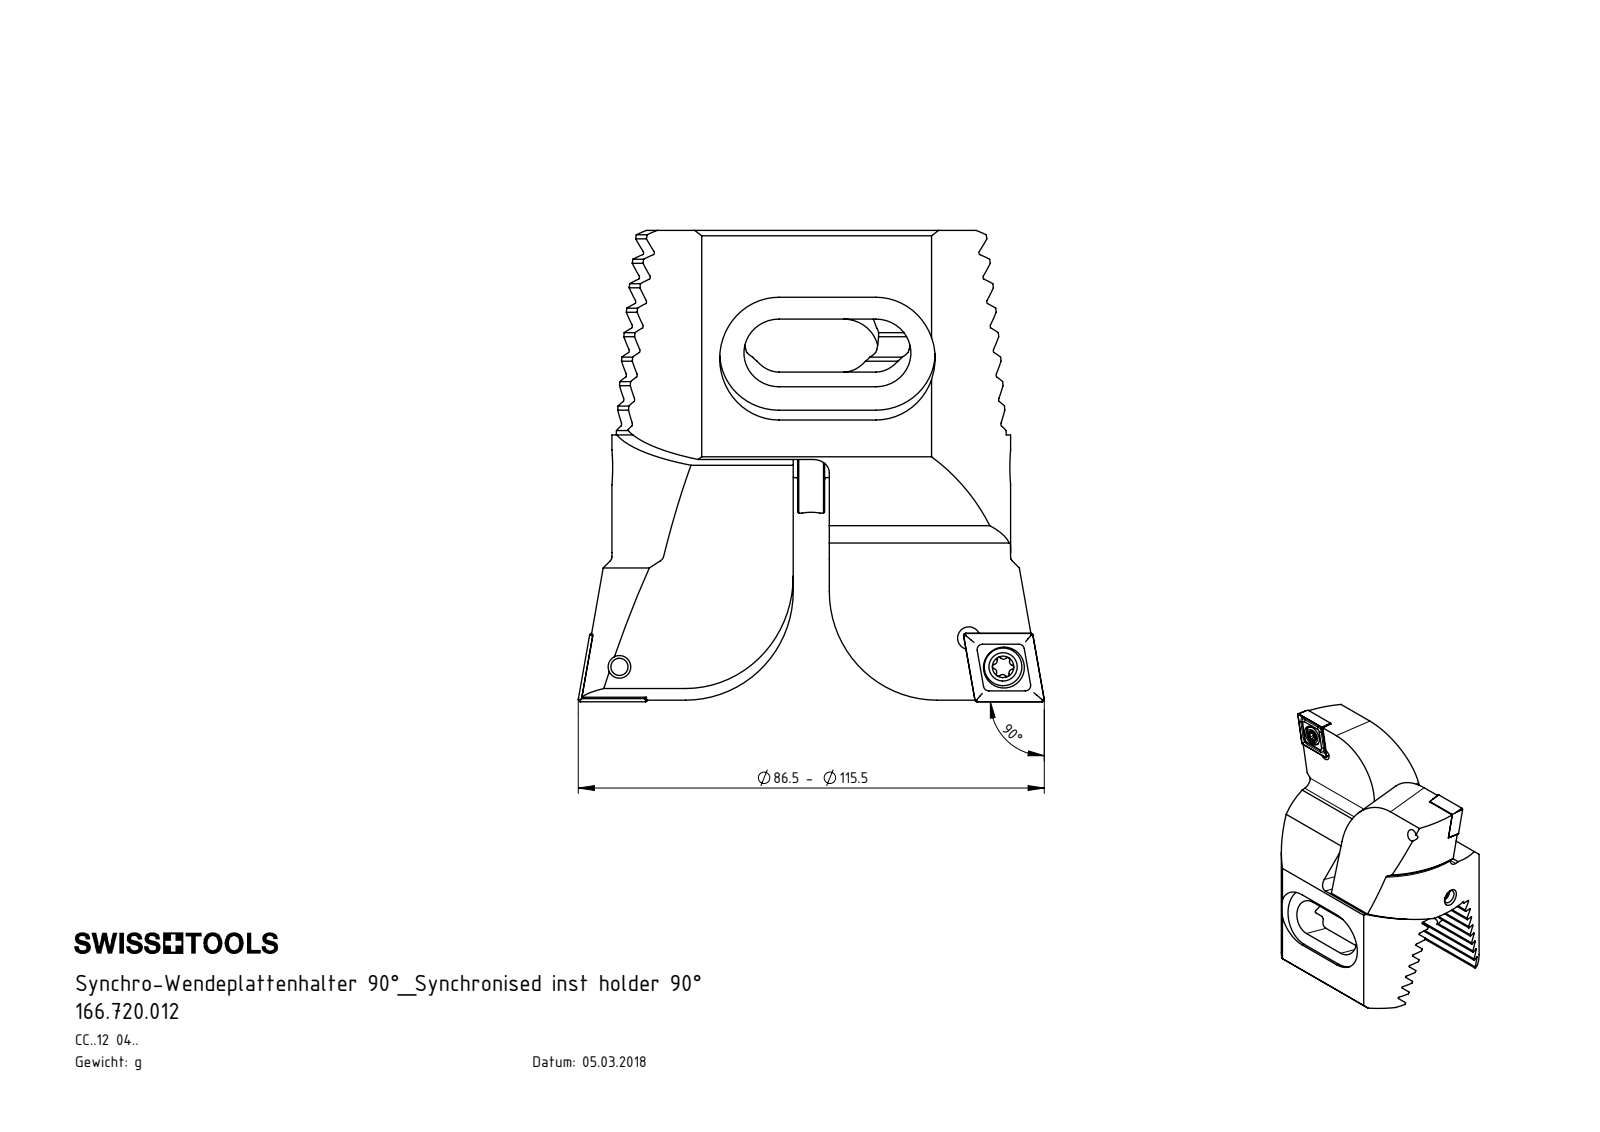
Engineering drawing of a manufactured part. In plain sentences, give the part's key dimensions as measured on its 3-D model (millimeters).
The part is named "166.720.012; Z72-ER3.000.068; ISO 4026 - M4 x 5; Z42-ER3.002.005_A (+4 more)". Its 3-D file was written by "SolidWorks 2017 (CONFIG_CONTROL_DESIGN)". It is 11 solids with 499 faces: 199 planar, 160 cylindrical and 140 other. Overall it measures 87.45 by 86.5 by 58 millimeters. Its volume is 146 963 cubic millimeters and its surface area 39 210 square millimeters. Round holes: 4 of diameter 4.2, 3 of diameter 3.3, 2 of diameter 1, 2 of diameter 5.5, 2 of diameter 7.6, 1 of diameter 5. Round bosses or shafts: 3 of diameter 4, 2 of diameter 7, 2 of diameter 5, 1 of diameter 17, 1 of diameter 6, 1 of diameter 3.8. Partial cylindrical surfaces (rounded edges, fillets, slot ends): 16 of radius 0.34, 12 of radius 0.39, 8 of radius 0.69, 8 of radius 1, 4 of radius 0.69, 4 of radius 3, 4 of radius 6.5, 4 of radius 11. The main face-to-face distances are 4.07, 8.14, 12.21, 16.28, 28.7, 29.3, 0.91, 24.43, 20.36, 58. The hole center spacings are 8.3, 8.5, 15, 65.08, 65.24, 71.37, 28.98, 58.5.
